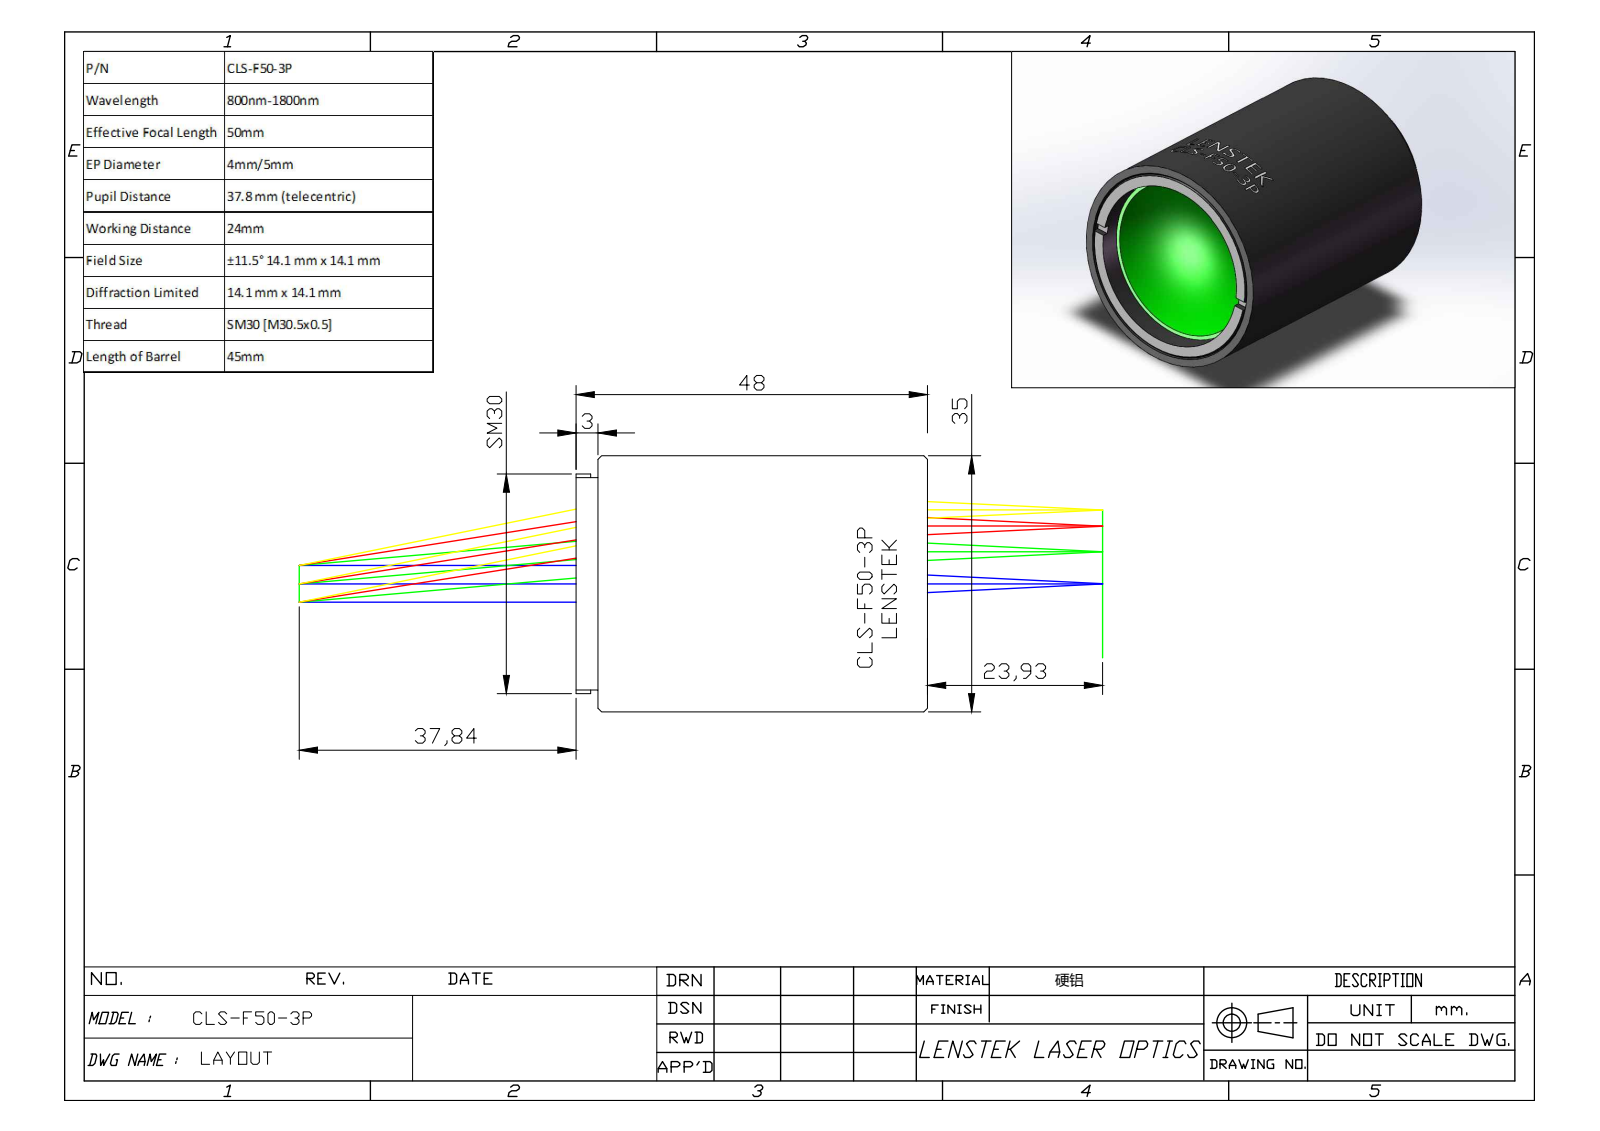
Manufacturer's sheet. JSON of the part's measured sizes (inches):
{"part_name": "CLS-F50-3P", "step_written_by": "SolidWorks 2018 (AUTOMOTIVE_DESIGN)", "units": "inches", "bodies": {"solids": 4, "faces": 450, "planar": 230, "cylindrical": 54, "other": 166}, "overall_size": [1.89, 1.378, 1.378], "volume_in3": 1.109, "surface_area_in2": 24.33, "round_holes": [[1.043, 1], [1.102, 1], [1.148, 1], [1.218, 1], [1.253, 1], [1.288, 1]], "round_bosses_or_shafts": [[1.378, 1], [1.26, 1], [1.22, 1], [1.201, 1], [1.169, 1], [1.142, 1]], "partial_cylinders_radius": [[0.689, 1]], "face_to_face_distances": [0.182, 1.708, 0.037, 1.685, 1.648, 0.098, 0.136, 1.783, 1.688, 1.59]}
